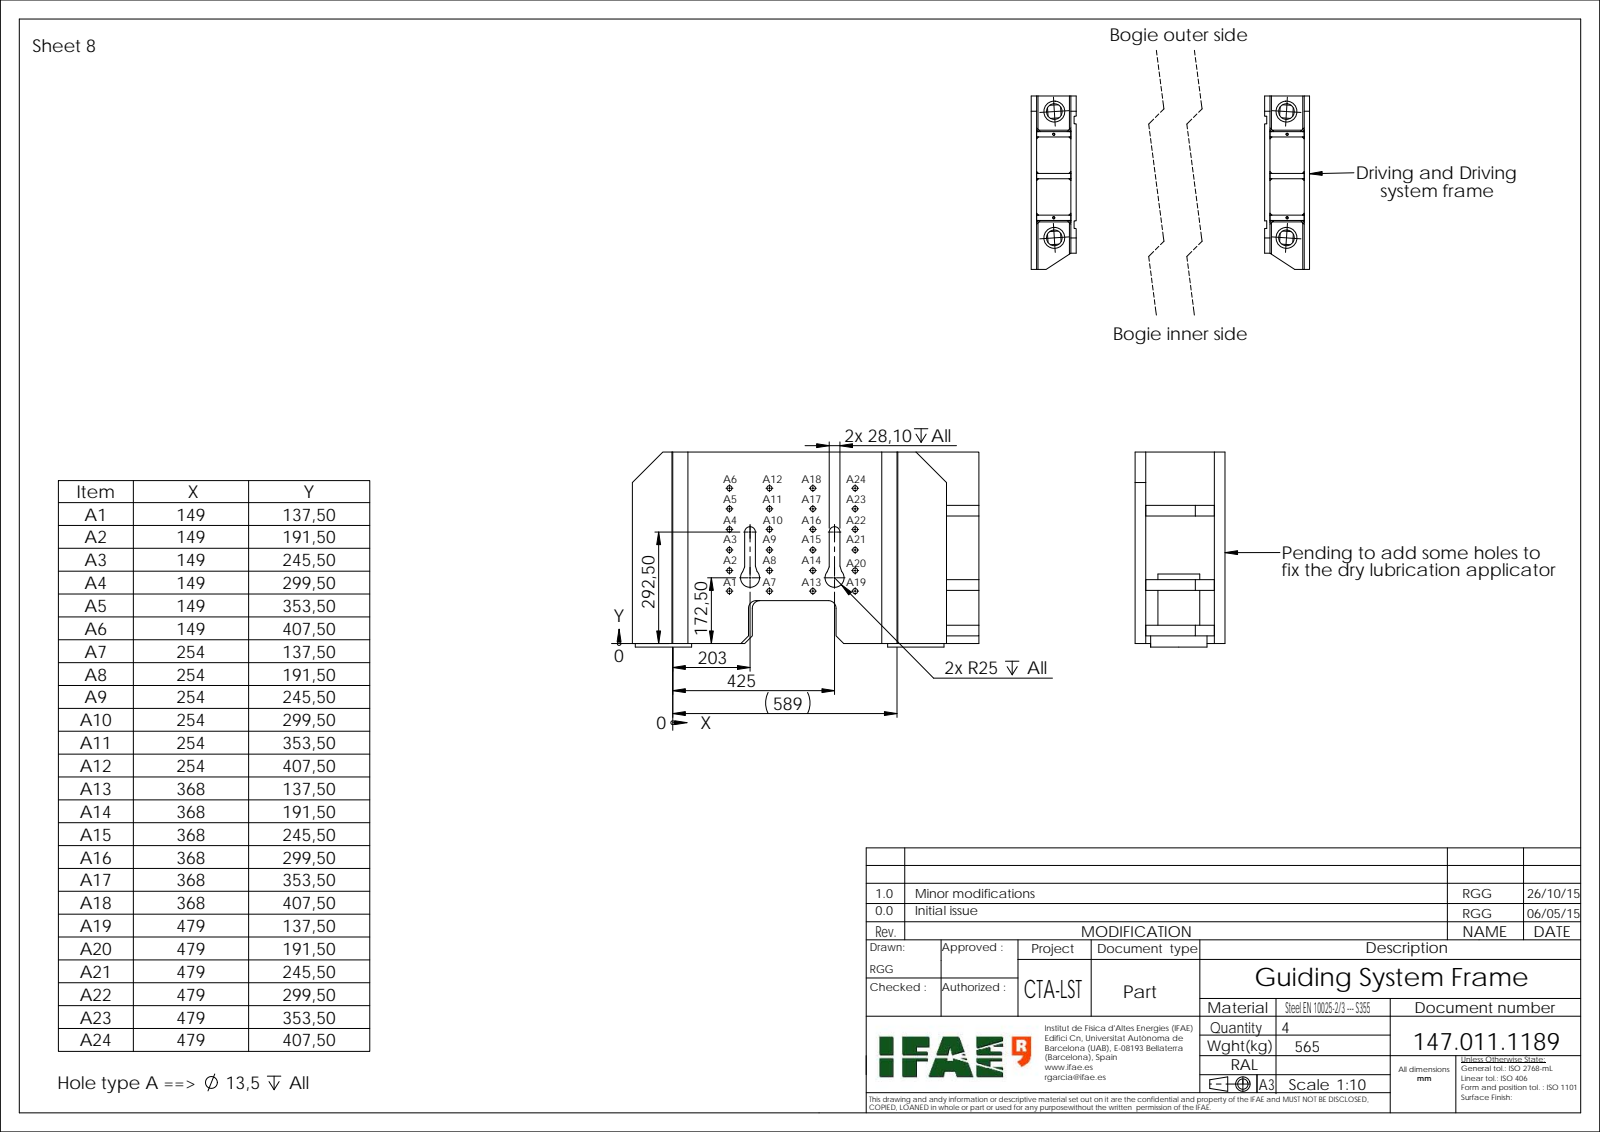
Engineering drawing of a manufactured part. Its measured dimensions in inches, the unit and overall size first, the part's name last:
Units: inches
Overall size (bounding box): 68.583 × 35.827 × 21.764
Round holes (diameter × count): ⌀0.531 ×24, ⌀0.402 ×4, ⌀3.228 ×4, ⌀4.331 ×4, ⌀5.827 ×4
Partial cylindrical surfaces — rounded edges, fillets, slot ends (radius × count): R0.787 ×4, R0.553 ×2, R0.984 ×2
Main face-to-face distances: 1.102, 59.291, 8.189, 7.087, 60.394, 67.48, 9.291, 58.189, 51.102, 8.622
Hole centre spacings: 2.126, 4.252, 6.378, 4.648, 4.86, 4.966, 8.88, 9.11
Volume: 4 341 in³ · Surface area: 11 450 in²
Bodies: 126 solids, 861 faces (756 planar, 97 cylindrical, 8 other)
Part name (STEP PRODUCT): 147.011.1189 20151026
STEP written by: SolidWorks 2014 (CONFIG_CONTROL_DESIGN)
